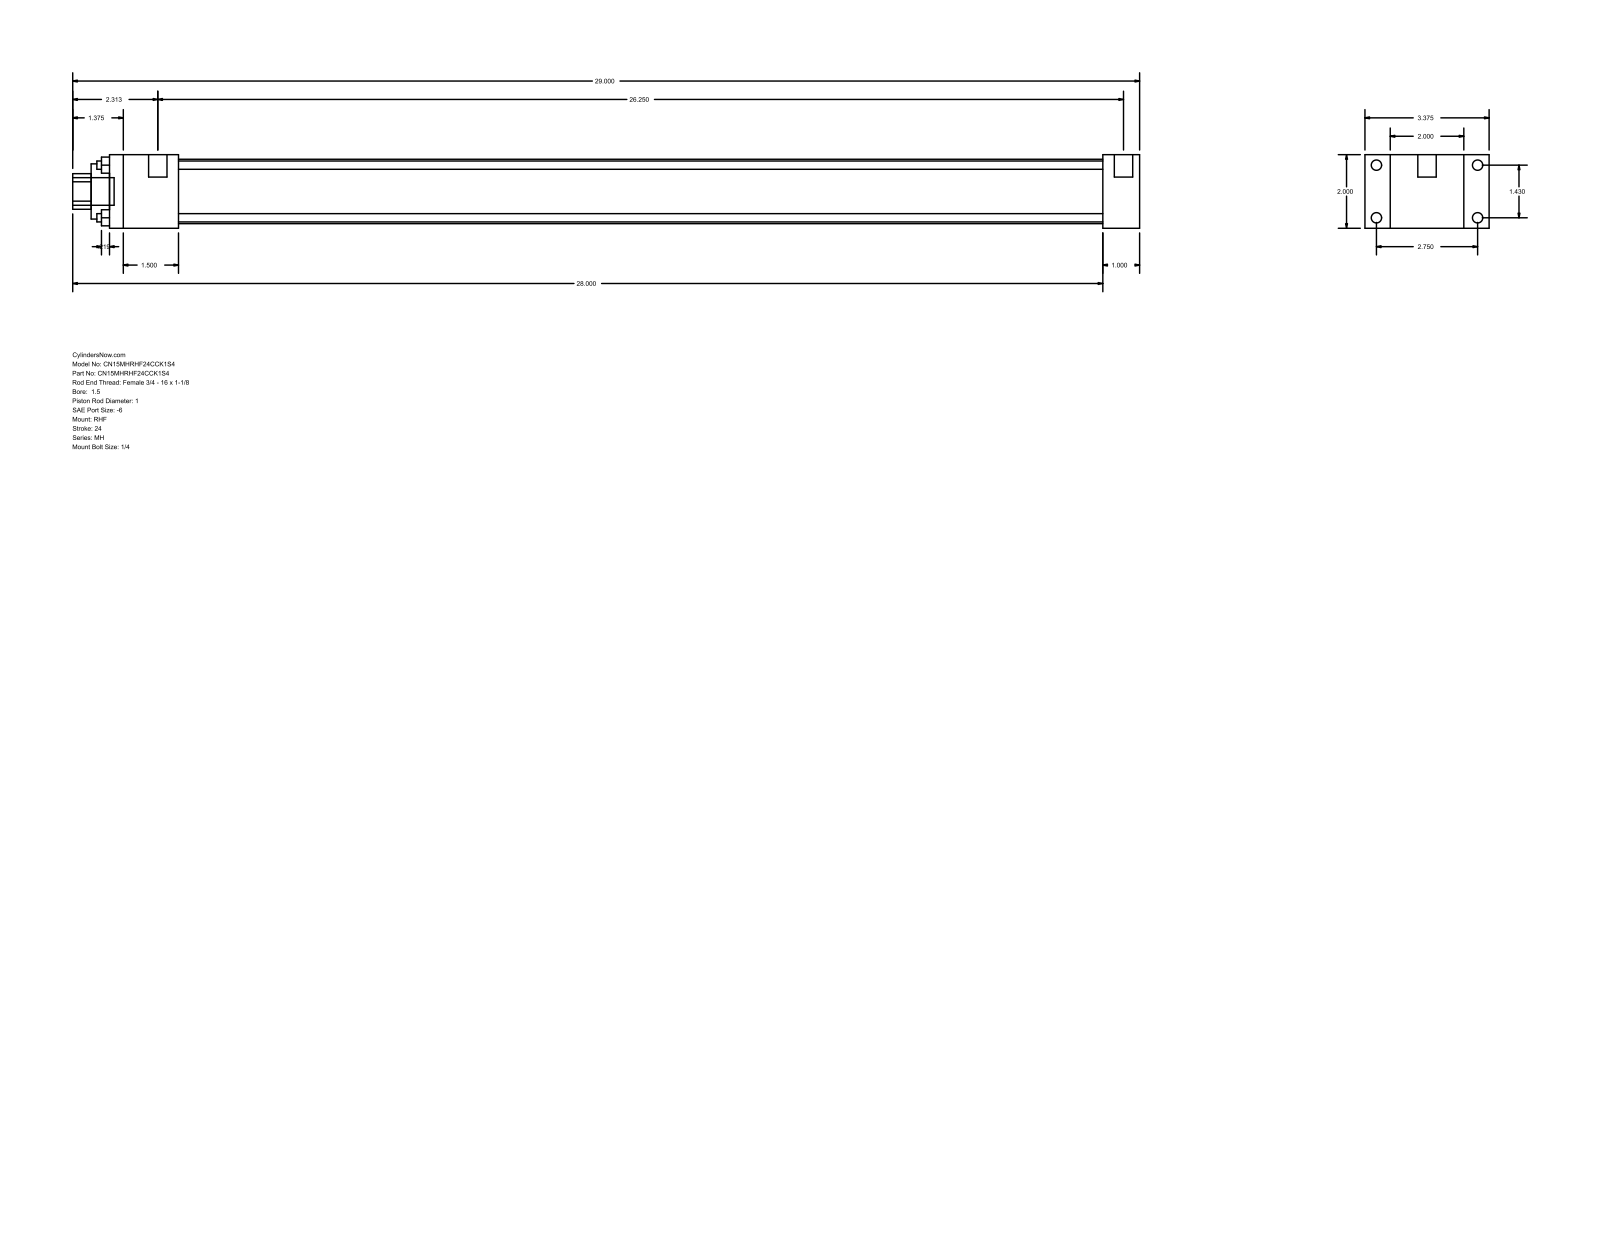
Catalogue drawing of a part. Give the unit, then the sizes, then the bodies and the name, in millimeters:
Units: millimetres
Overall size (bounding box): 736.6 × 85.72 × 50.8
Round holes (diameter × count): ⌀5.71 ×4, ⌀25.4 ×1, ⌀38.1 ×1, ⌀44.45 ×1
Round bosses / shafts (diameter × count): ⌀7.14 ×4, ⌀5.56 ×4, ⌀12.7 ×2, ⌀19.05 ×1
Partial cylindrical surfaces — rounded edges, fillets, slot ends (radius × count): R12.29 ×1
Main face-to-face distances: 50.8, 25.4, 17.46, 68.26, 85.72, 711.2, 685.8, 47.63, 638.17, 663.57
Hole centre spacings: 25.68, 36.32, 51.36
Bodies: 0 solids, 88 faces (60 planar, 28 cylindrical, 0 other)
Part name (STEP PRODUCT): MH_RHF__0150_1
STEP written by: GSSL Pune (CONFIG_CONTROL_DESIGN)
